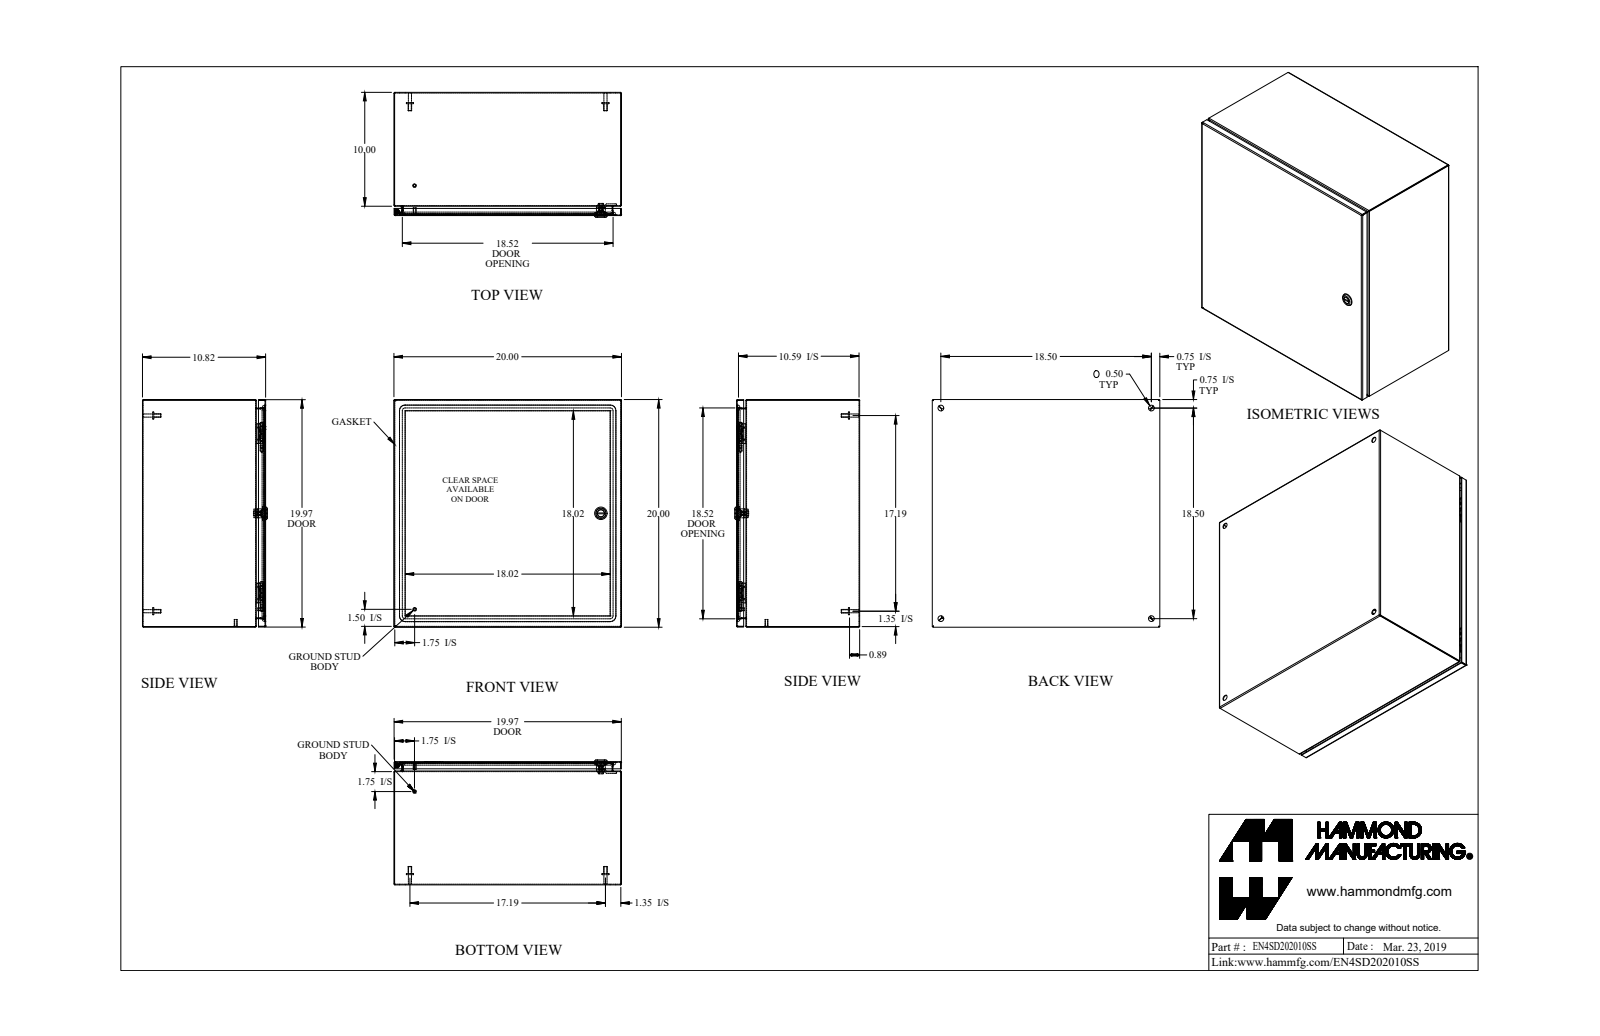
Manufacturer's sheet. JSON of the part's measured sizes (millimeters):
{"part_name": "EN4SD202010SS_Default", "step_written_by": "SolidWorks 2019 (CONFIG_CONTROL_DESIGN)", "units": "millimeters", "bodies": {"solids": 22, "faces": 657, "planar": 303, "cylindrical": 212, "other": 142}, "overall_size": [508, 508, 278.9], "volume_mm3": 1768000, "surface_area_mm2": 2381000, "round_holes": [[12.7, 5], [4.4, 1], [5, 1], [6.1, 1], [6.1, 1], [9.8, 1], [16, 1], [19.5, 1]], "round_bosses_or_shafts": [[8, 6], [15.9, 5], [7, 4], [6.4, 2], [27.9, 1], [19.9, 1], [13.3, 1], [11.6, 1]], "partial_cylinders_radius": [[0.7, 21], [2.2, 21], [4.8, 12], [0.2, 4], [1.6, 4], [6.4, 4], [12.7, 4], [3.2, 2]], "face_to_face_distances": [1.4, 273.4, 506.6, 505.1, 272, 274.9, 508, 20.9, 252.6, 19], "hole_center_spacings": [469.9, 236.5, 501.4, 664.5]}
